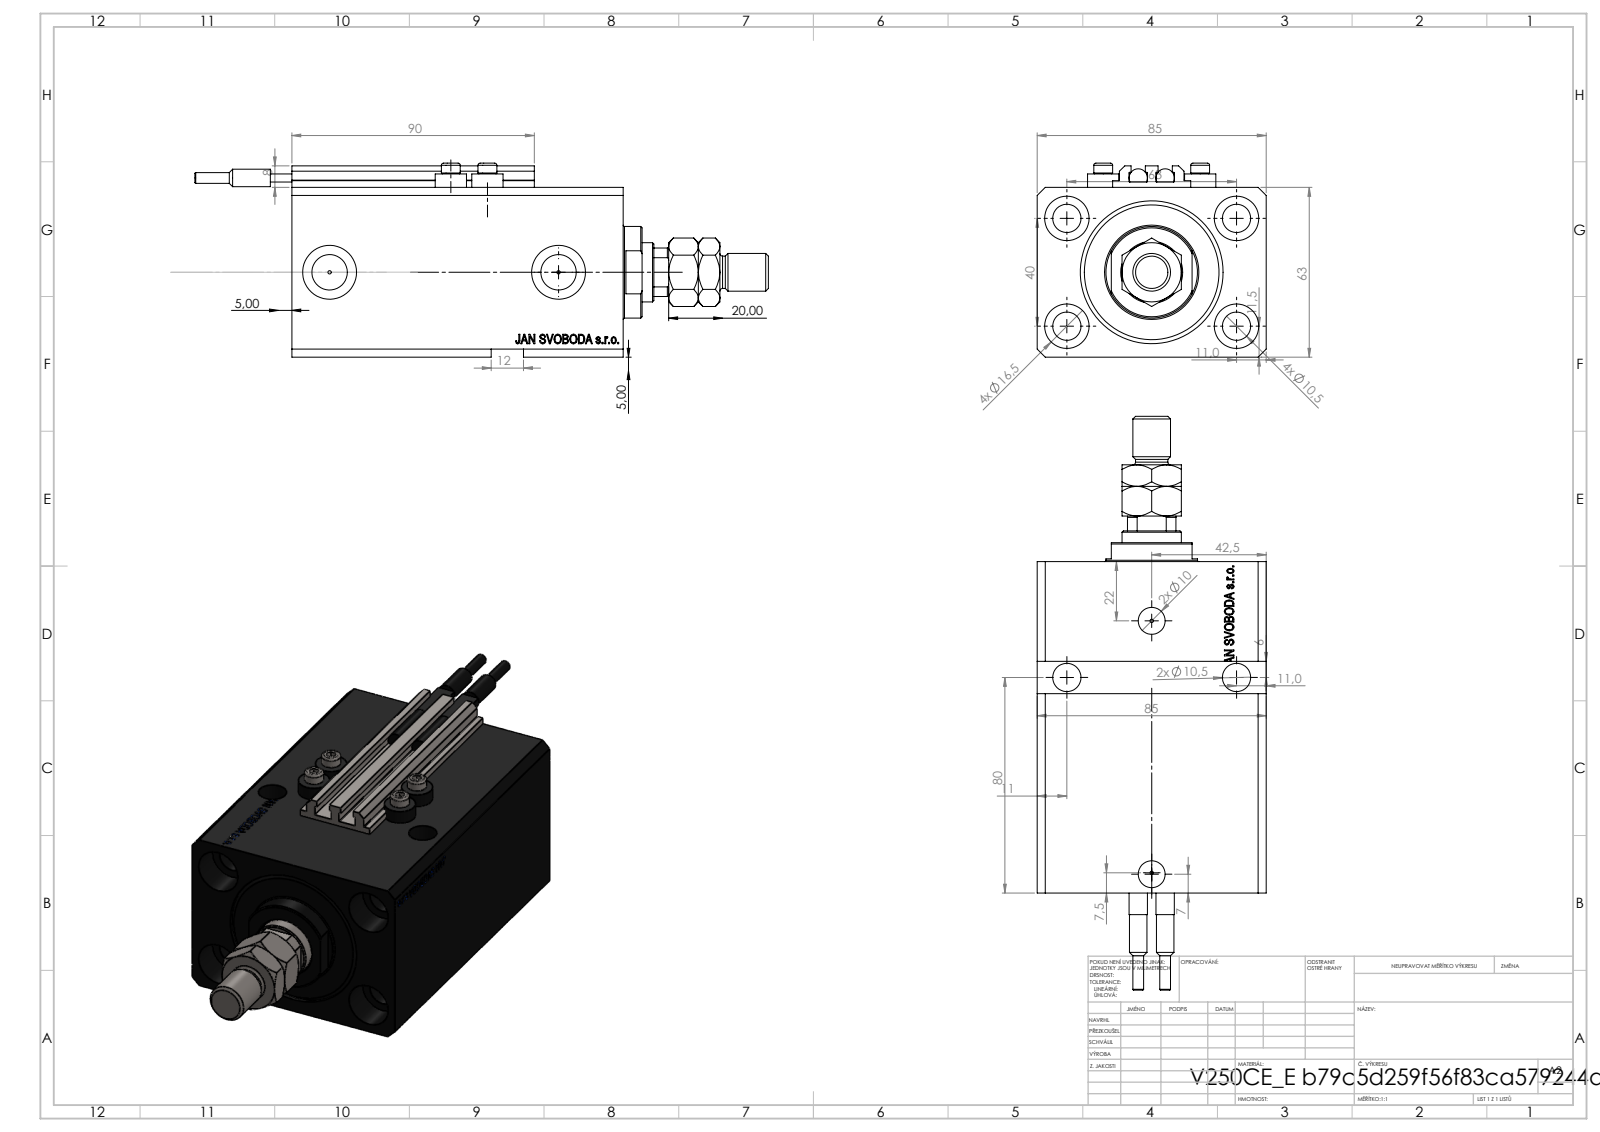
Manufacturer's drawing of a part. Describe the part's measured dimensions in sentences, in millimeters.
The part is named "ALLEN BOLT V250CE; V250CE_C_VCP; V250CE_VC_E; V250CE_E_Body (+2 more)". Its 3-D file was written by "SolidWorks 2019 (CONFIG_CONTROL_DESIGN)". It is 11 solids with 1208 faces: 582 planar, 162 cylindrical and 464 other. Overall it measures 213 by 85 by 72 millimeters. Its volume is 570 751 cubic millimeters and its surface area 125 119 square millimeters. Round holes: 8 of diameter 10.5, 4 of diameter 1.25, 4 of diameter 4, 4 of diameter 16.5, 2 of diameter 10, 2 of diameter 13.16, 2 of diameter 20, 1 of diameter 12.5, 1 of diameter 22, 1 of diameter 40, 1 of diameter 53. Round bosses or shafts: 4 of diameter 11.6, 4 of diameter 7, 2 of diameter 6.8, 2 of diameter 6.5, 2 of diameter 4, 1 of diameter 34, 1 of diameter 14, 1 of diameter 12. Partial cylindrical surfaces (rounded edges, fillets, slot ends): 10 of radius 0.2, 1 of radius 10.5. The main face-to-face distances are 63, 85, 17, 123, 106, 3, 11.4, 94.6, 111.6, 65. The hole center spacings are 37.31, 63, 13.6, 15.4, 24.96, 27.54, 33.62, 36.
